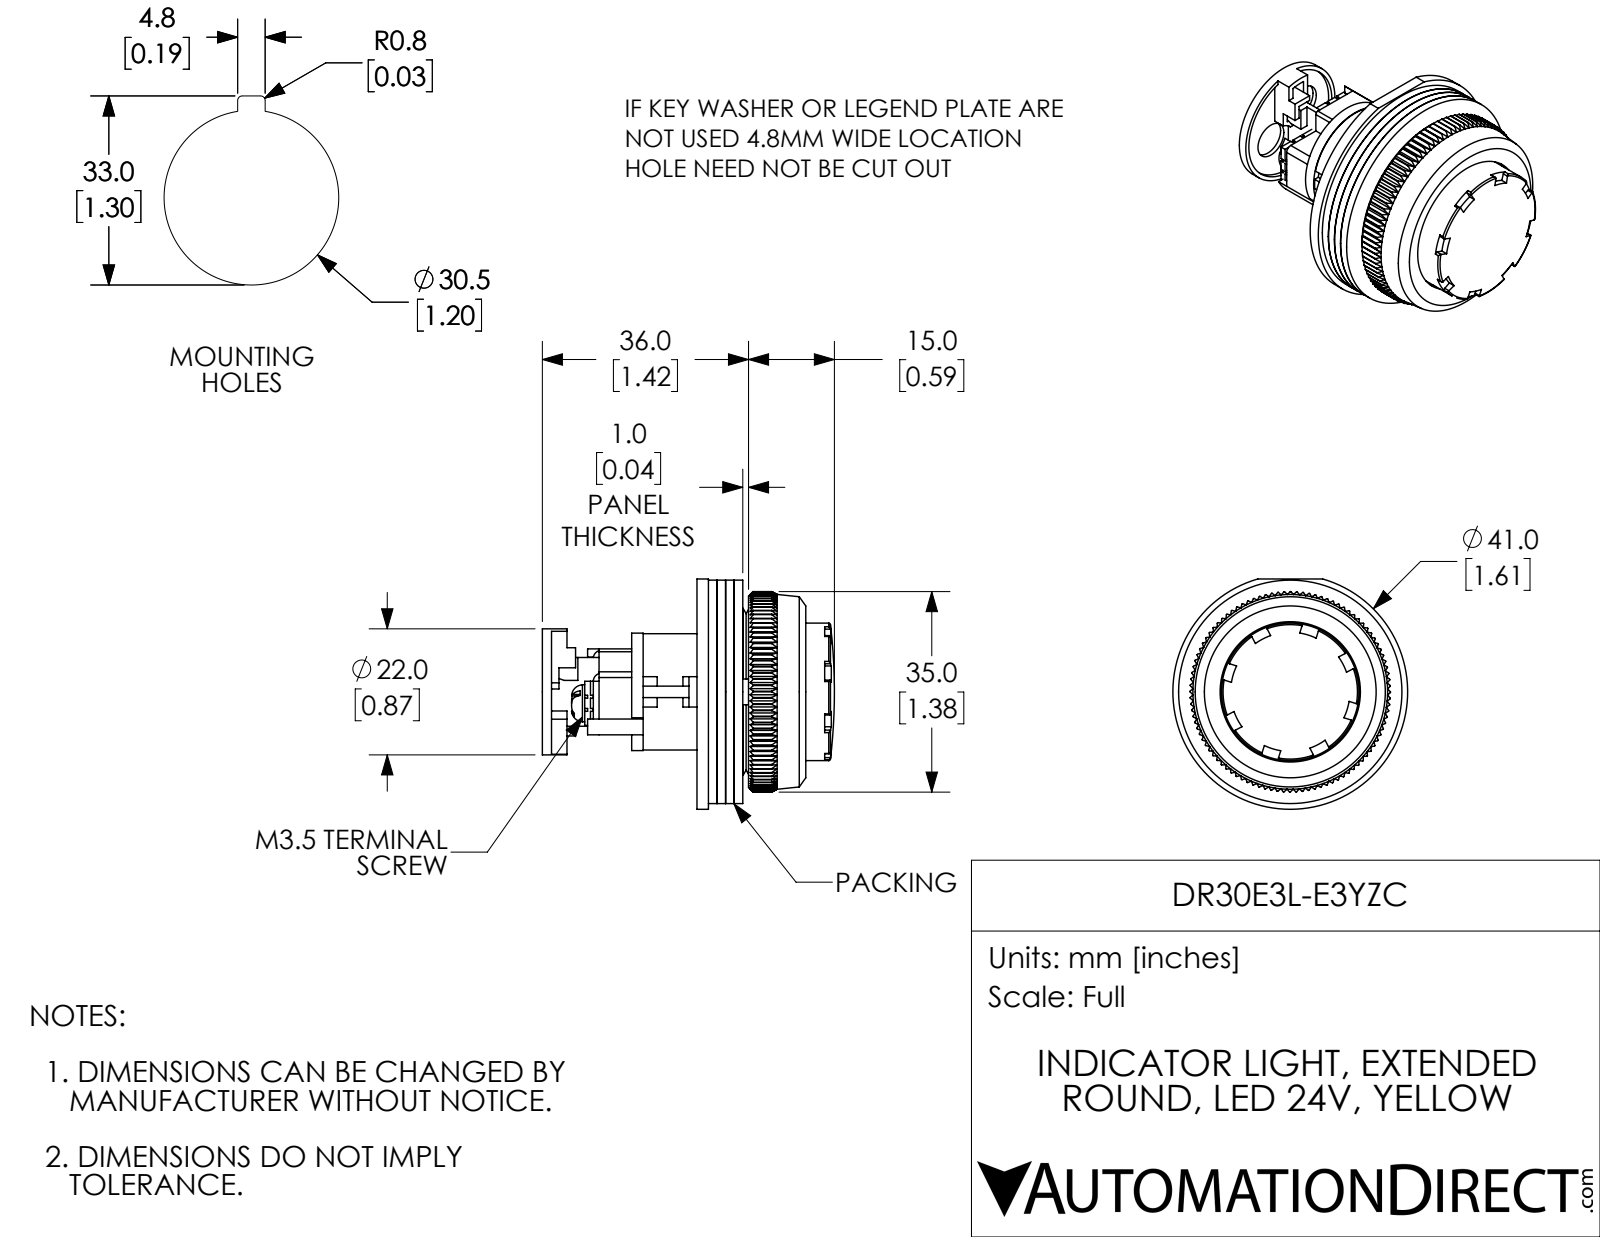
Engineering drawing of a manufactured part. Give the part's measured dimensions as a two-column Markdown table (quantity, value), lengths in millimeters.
| quantity | value |
| --- | --- |
| part name | DR30E3L-E3YZC |
| STEP written by | SolidWorks 2017 (AUTOMOTIVE_DESIGN) |
| units | millimeters |
| bodies | 16 solids, 1287 faces (717 planar, 328 cylindrical, 242 other) |
| overall size | 51 × 41 × 40.2 |
| volume | 17 570 mm³ |
| surface area | 24 230 mm² |
| round holes (diameter × count) | 3 × 2, 3.5 × 2, 6.4 × 2, 14.3 × 1, 16 × 1, 18.3 × 1, 20 × 1, 20.5 × 1, 22 × 1, 24.5 × 1, 28.5 × 1, 29.8 × 1 |
| round bosses / shafts (diameter × count) | 1.6 × 2, 41 × 1, 39 × 1, 29.5 × 1, 24 × 1, 21.8 × 1, 20.8 × 1, 20.3 × 1 |
| partial cylindrical surfaces (radius × count) | 0.3 × 16, 1.5 × 8, 0.3 × 5, 0.6 × 5, 0.4 × 4, 1.4 × 4, 0.5 × 2, 1 × 2 |
| main face-to-face distances | 1.5, 3, 4.5, 1, 5, 2, 8, 6.5, 2.5, 6 |
| hole center spacings | 4.5, 4.7, 9.2, 8.9, 9.4 |
